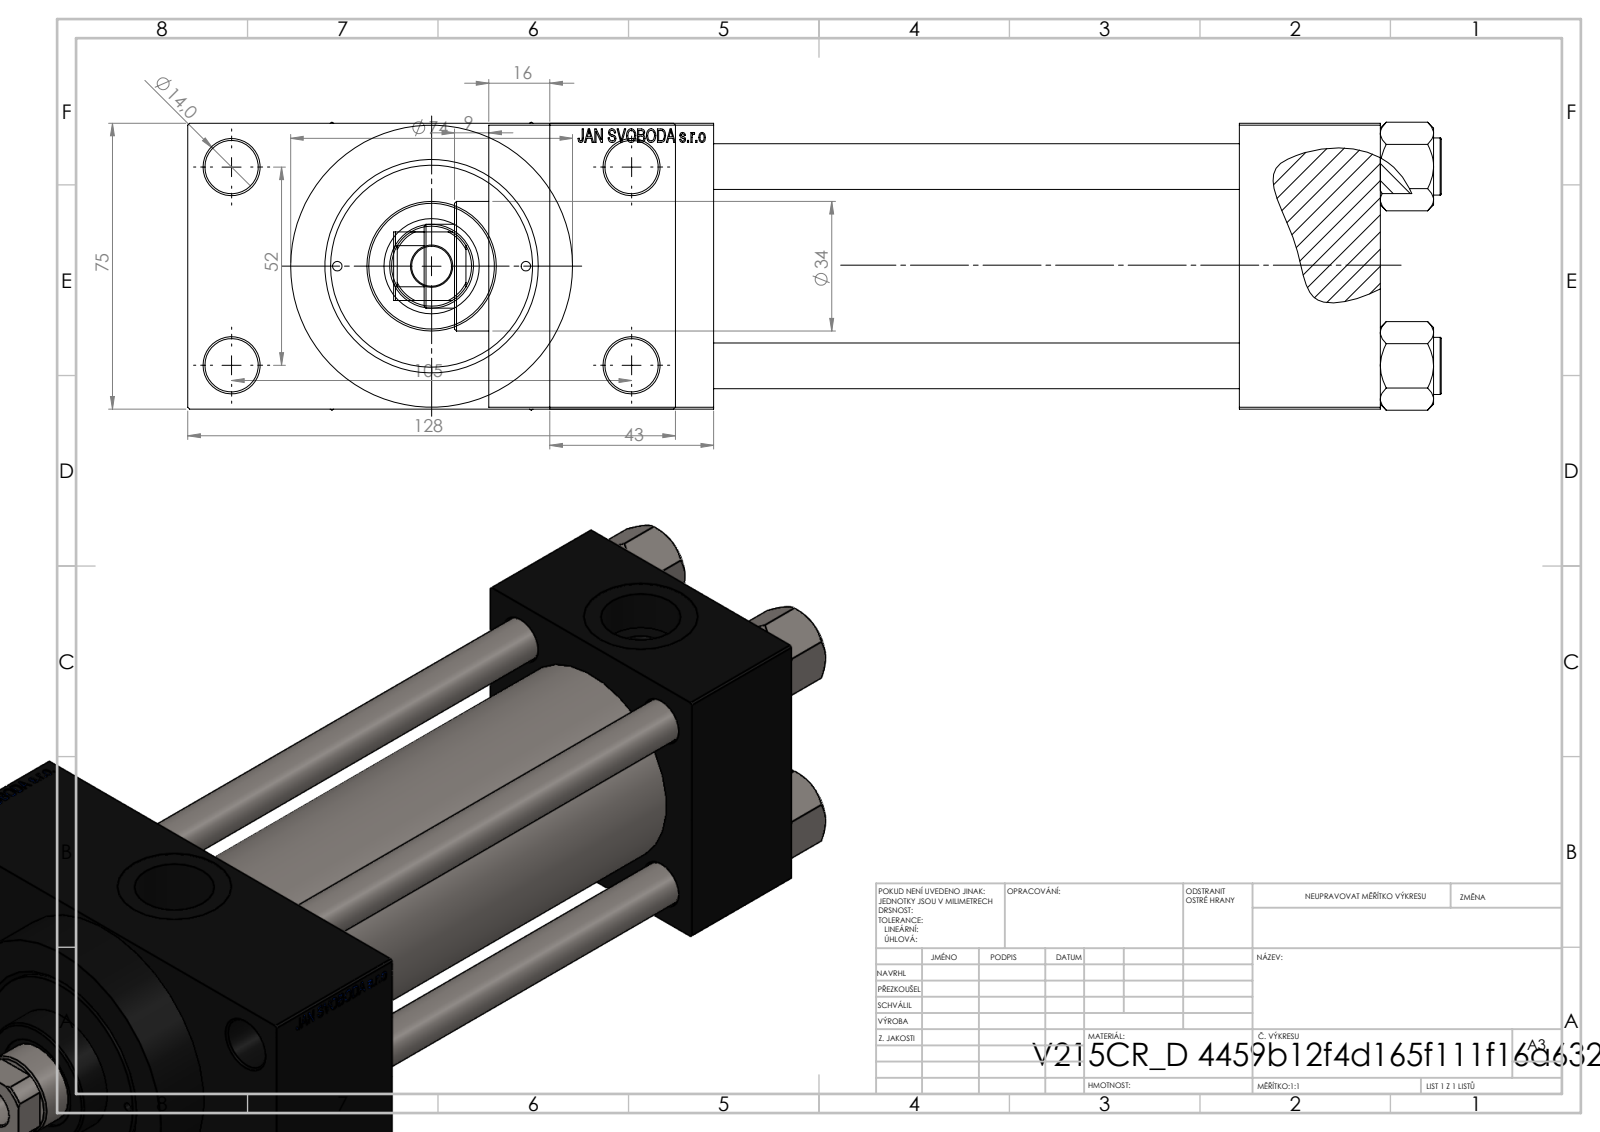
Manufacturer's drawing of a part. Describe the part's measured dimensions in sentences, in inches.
The part is named "V215CR_D_Body; V215_VC_A; NUT_M5_D; V215CR_D_TYCINKA (+1 more)". Its 3-D file was written by "SolidWorks 2019 (CONFIG_CONTROL_DESIGN)". It is 11 solids with 1112 faces: 499 planar, 93 cylindrical and 520 other. Overall it measures 10.827 by 5.039 by 2.974 inches. Its volume is 55.71 cubic inches and its surface area 324.1 square inches. Round holes: 4 of diameter 0.472, 4 of diameter 0.551, 2 of diameter 0.098, 2 of diameter 0.276, 2 of diameter 0.825, 2 of diameter 1.181, 1 of diameter 0.413, 1 of diameter 0.866, 1 of diameter 0.984, 1 of diameter 1.614, 1 of diameter 1.969, 1 of diameter 2.087. Round bosses or shafts: 4 of diameter 0.591, 1 of diameter 2.913, 1 of diameter 2.205, 1 of diameter 1.339. Partial cylindrical surfaces (rounded edges, fillets, slot ends): 1 of radius 0.413. The main face-to-face distances are 2.953, 5.433, 1.457, 6.89, 1.043, 3.996, 8.583, 7.126, 1.693, 0.63. The hole center spacings are 1.031, 1.037, 1.456, 1.497, 2.059, 2.253, 2.3, 2.307.
